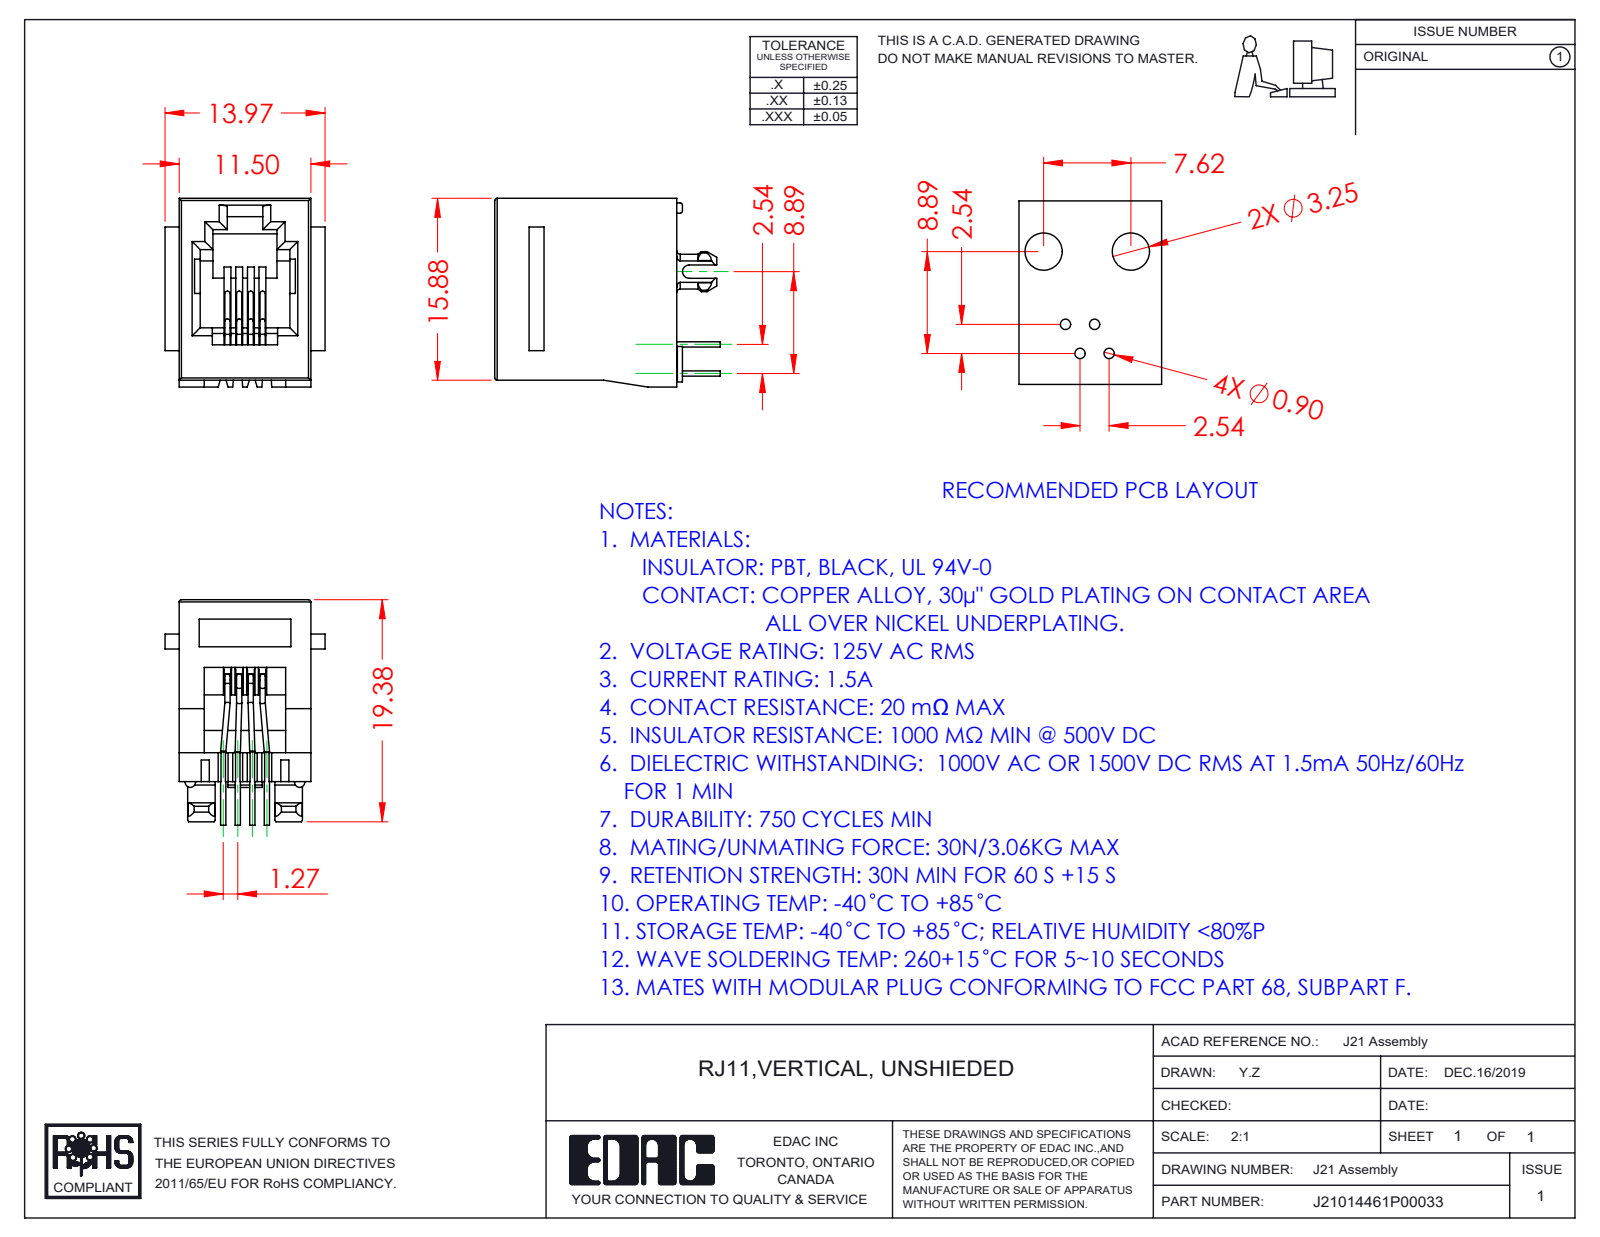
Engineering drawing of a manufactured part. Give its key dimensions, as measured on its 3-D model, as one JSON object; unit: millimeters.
{"part_name": "21 Contacts; RJ21014461P00033; 21 Insulator", "step_written_by": "SolidWorks 2016 (CONFIG_CONTROL_DESIGN)", "units": "millimeters", "bodies": {"solids": 5, "faces": 369, "planar": 230, "cylindrical": 111, "other": 28}, "overall_size": [19.68, 16.48, 13.97], "volume_mm3": 1616, "surface_area_mm2": 2564, "round_holes": [[2, 2]], "round_bosses_or_shafts": [[0.46, 24]], "partial_cylinders_radius": [[0.5, 9], [0.7, 9], [0.2, 7], [0.23, 4], [0.45, 2], [1.52, 2], [1.75, 2], [0.57, 1]], "face_to_face_distances": [11.5, 1.6, 15.88, 1.02, 7.2, 0.6, 2.95, 8.55, 2.04, 1.35], "hole_center_spacings": [8.4]}
